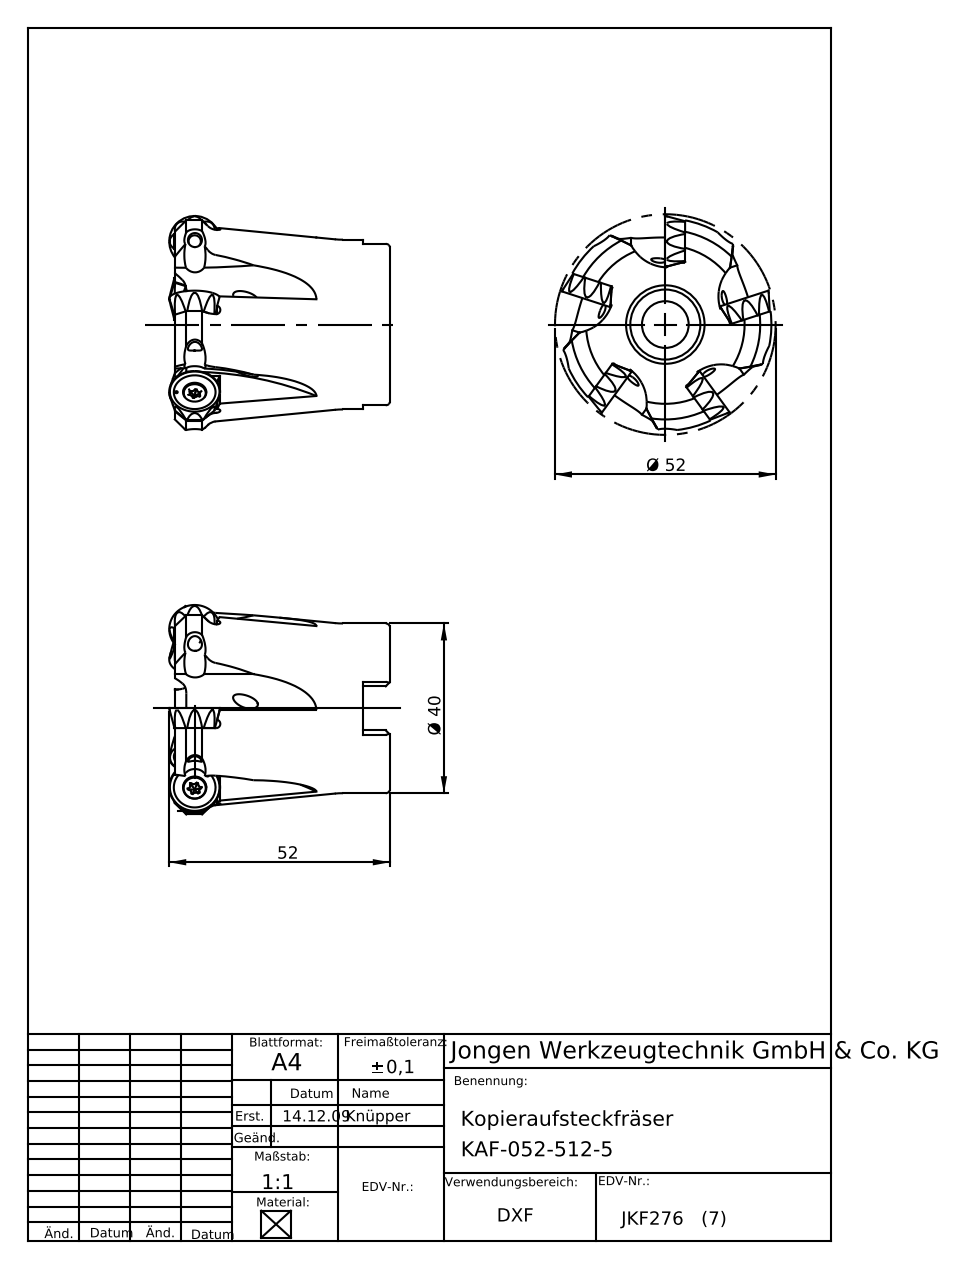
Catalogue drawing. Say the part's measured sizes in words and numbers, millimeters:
The part is named "KAF-052-512-5". Its 3-D file was written by "SolidWorks 2013 (AUTOMOTIVE_DESIGN)". It is 1 solid with 116 faces: 65 planar, 16 cylindrical and 35 other. Overall it measures 51.99 by 51.95 by 51.95 millimeters. Its volume is 64 851 cubic millimeters and its surface area 15 866 square millimeters. Round holes: 5 of diameter 3, 1 of diameter 11, 1 of diameter 16.5, 1 of diameter 21.85, 1 of diameter 22.15, 1 of diameter 22.3. Round bosses or shafts: 1 of diameter 46. Partial cylindrical surfaces (rounded edges, fillets, slot ends): 5 of radius 1. The main face-to-face distances are 47.95, 6.3, 41.65, 23, 16.7, 24.95, 5.49, 10.4, 4.91, 34.95.
